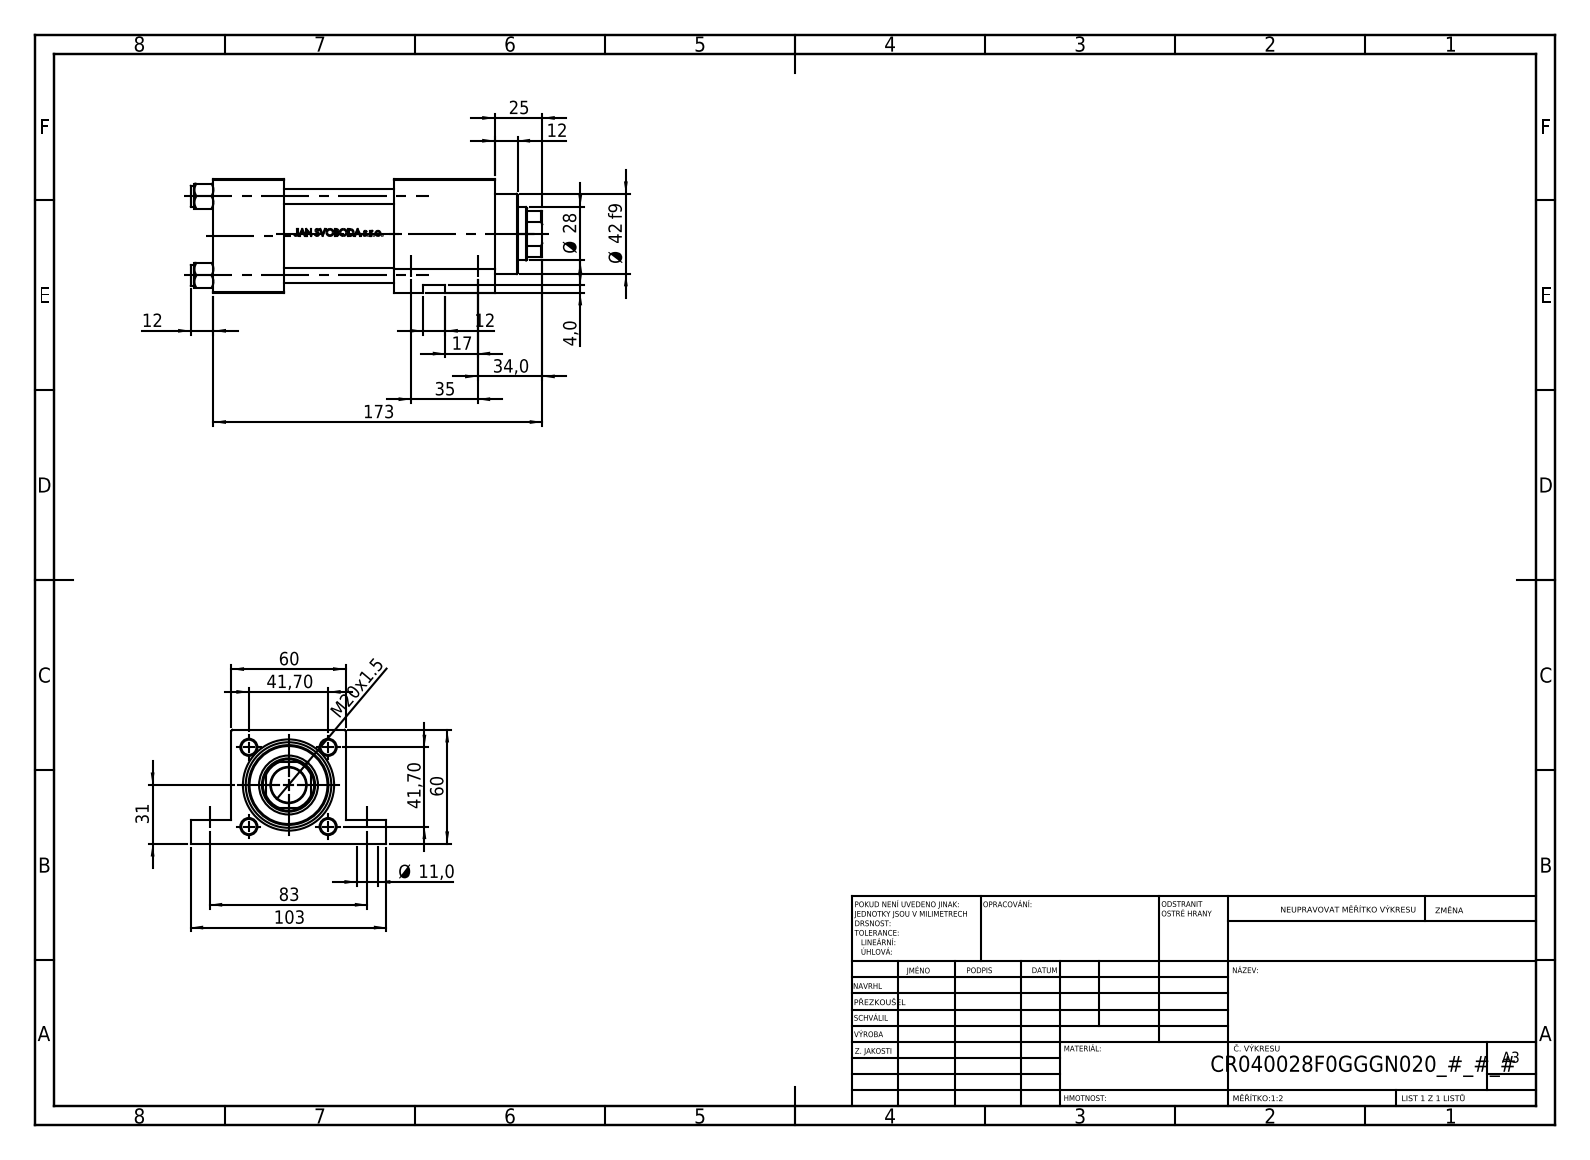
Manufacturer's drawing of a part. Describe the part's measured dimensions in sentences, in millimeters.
The part is named "NUT_M5_F; V215CR_F_TYCINKA; V215CR_F_Body; V215_VC_A (+1 more)". Its 3-D file was written by "SolidWorks 2019 (CONFIG_CONTROL_DESIGN)". It is 11 solids with 1121 faces: 438 planar, 143 cylindrical and 540 other. Overall it measures 185 by 103 by 60 millimeters. Its volume is 444 851 cubic millimeters and its surface area 117 845 square millimeters. Round holes: 4 of diameter 8, 2 of diameter 7, 2 of diameter 11, 2 of diameter 11, 2 of diameter 16.66, 2 of diameter 24, 1 of diameter 18.5, 1 of diameter 28, 1 of diameter 31, 1 of diameter 40, 1 of diameter 45. Round bosses or shafts: 4 of diameter 11, 1 of diameter 46, 1 of diameter 42. Partial cylindrical surfaces (rounded edges, fillets, slot ends): 1 of radius 13.5. The main face-to-face distances are 60, 37, 95, 58, 148, 111, 53, 12.5, 47.5, 38. The hole center spacings are 41.7, 28.79, 30.2, 35, 42.09, 50.06, 58.97, 83.
